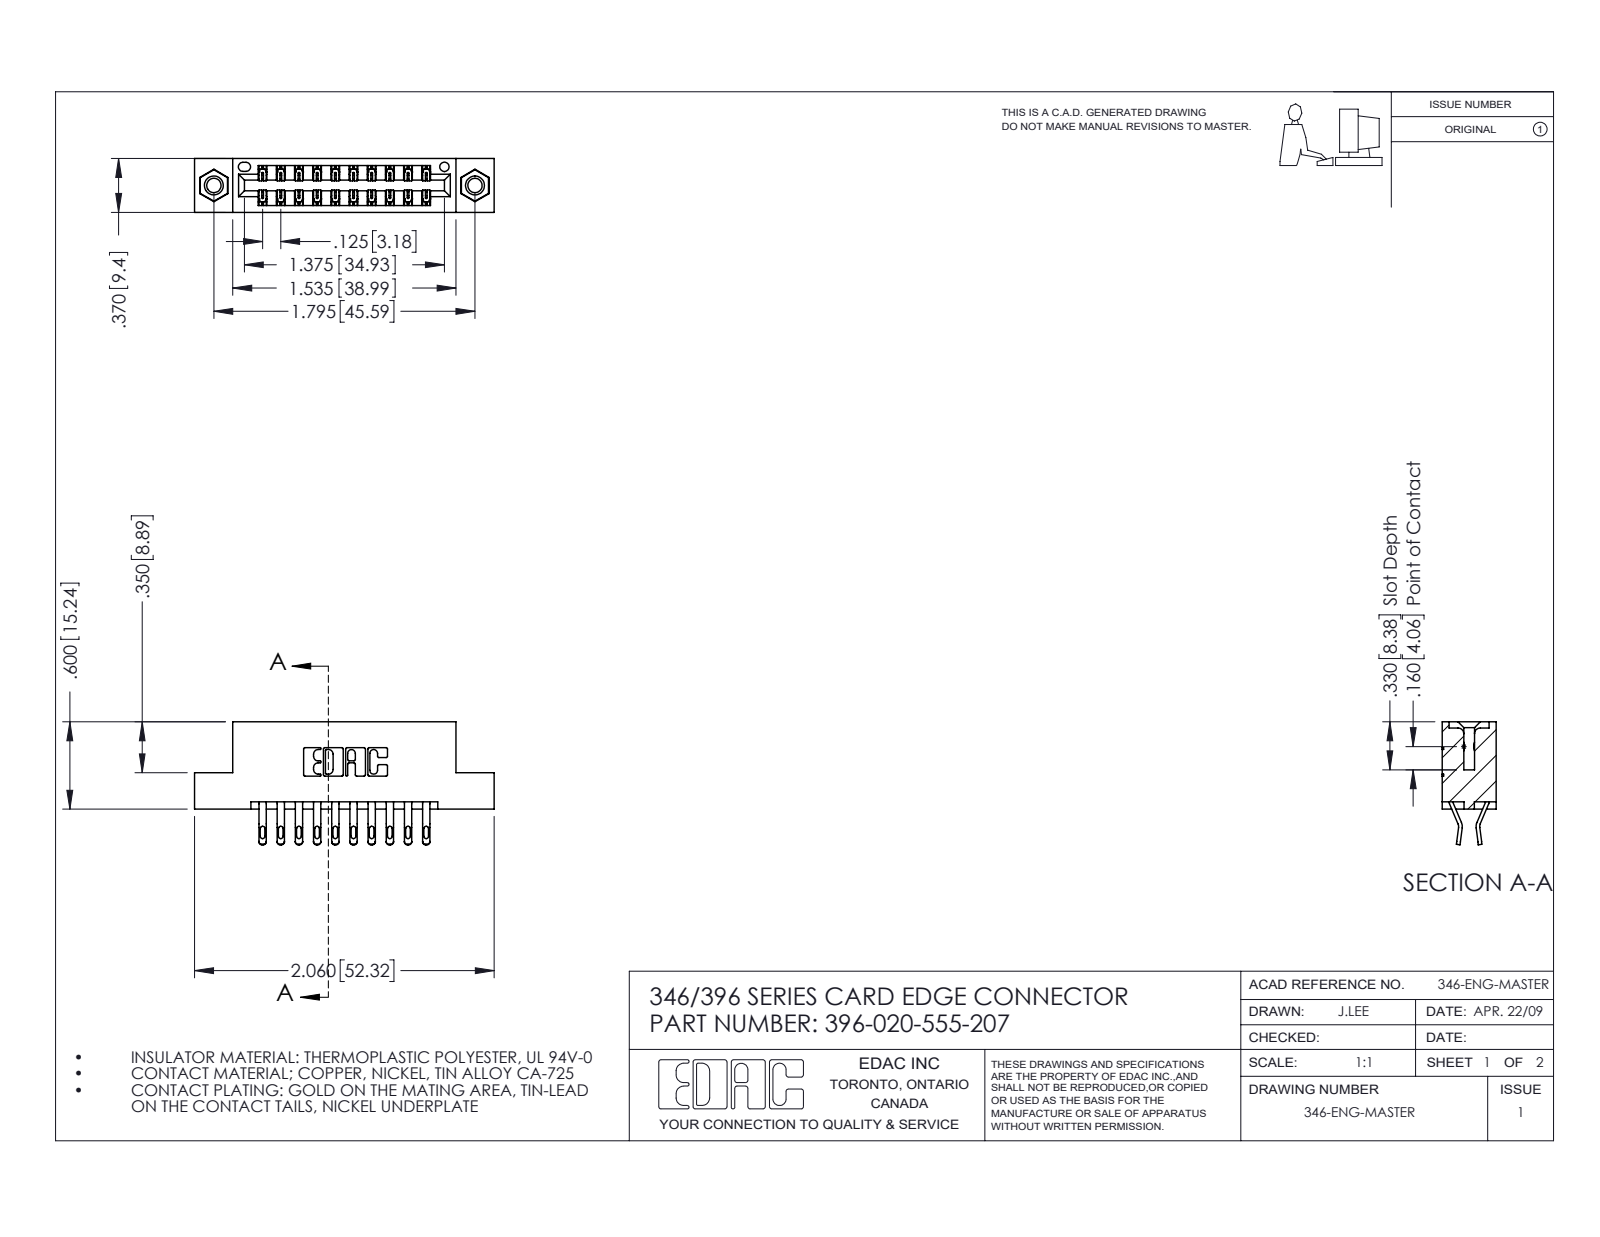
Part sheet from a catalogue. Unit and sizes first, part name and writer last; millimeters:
Units: millimetres
Overall size (bounding box): 52.3 × 21.5 × 9.4
Round holes (diameter × count): ⌀2.5 ×2, ⌀3.2 ×2, ⌀4 ×2, ⌀1.6 ×1
Round bosses / shafts (diameter × count): ⌀3.9 ×2
Partial cylindrical surfaces — rounded edges, fillets, slot ends (radius × count): R0.4 ×40, R0.5 ×40, R0.2 ×30, R0.3 ×22, R0.2 ×6, R0.8 ×6, R0.7 ×3, R0.3 ×2
Main face-to-face distances: 6.4, 1.2, 8.2, 9.4, 0.6, 1.8, 7.6, 7, 3.8, 5.6
Hole centre spacings: 6.2, 40.4, 45.6
Volume: 4 900 mm³ · Surface area: 6 471 mm²
Bodies: 23 solids, 1342 faces (768 planar, 558 cylindrical, 16 other)
Part name (STEP PRODUCT): 396-020-555-207; 345-250-001_345-250-005-103; 345-292-001_555 Tail; 346 Part_Flush Mounting Lugs - 0.156 Dia-TI
STEP written by: SolidWorks 2016 (CONFIG_CONTROL_DESIGN)
